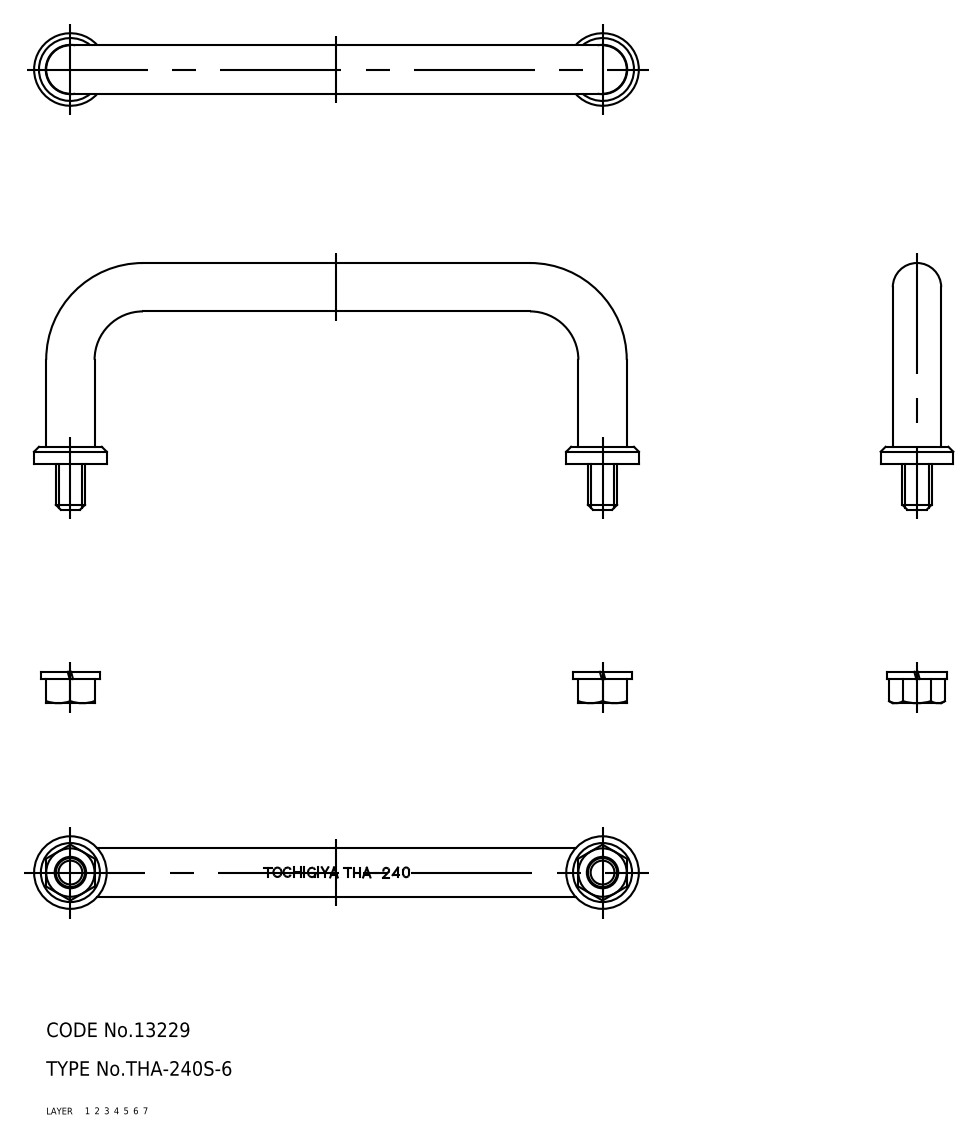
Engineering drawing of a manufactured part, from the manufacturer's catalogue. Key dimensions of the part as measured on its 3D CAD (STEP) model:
Part name (STEP PRODUCT): facing ring; nut; washer; pull (+1 more)
STEP written by: CADfix (AUTOMOTIVE_DESIGN)
Units: millimetres
Bodies: 7 solids, 80 faces (0 planar, 0 cylindrical, 80 other)
Overall size (bounding box): 125 × 51 × 15
Volume: 15 401 mm³ · Surface area: 8 122 mm²
